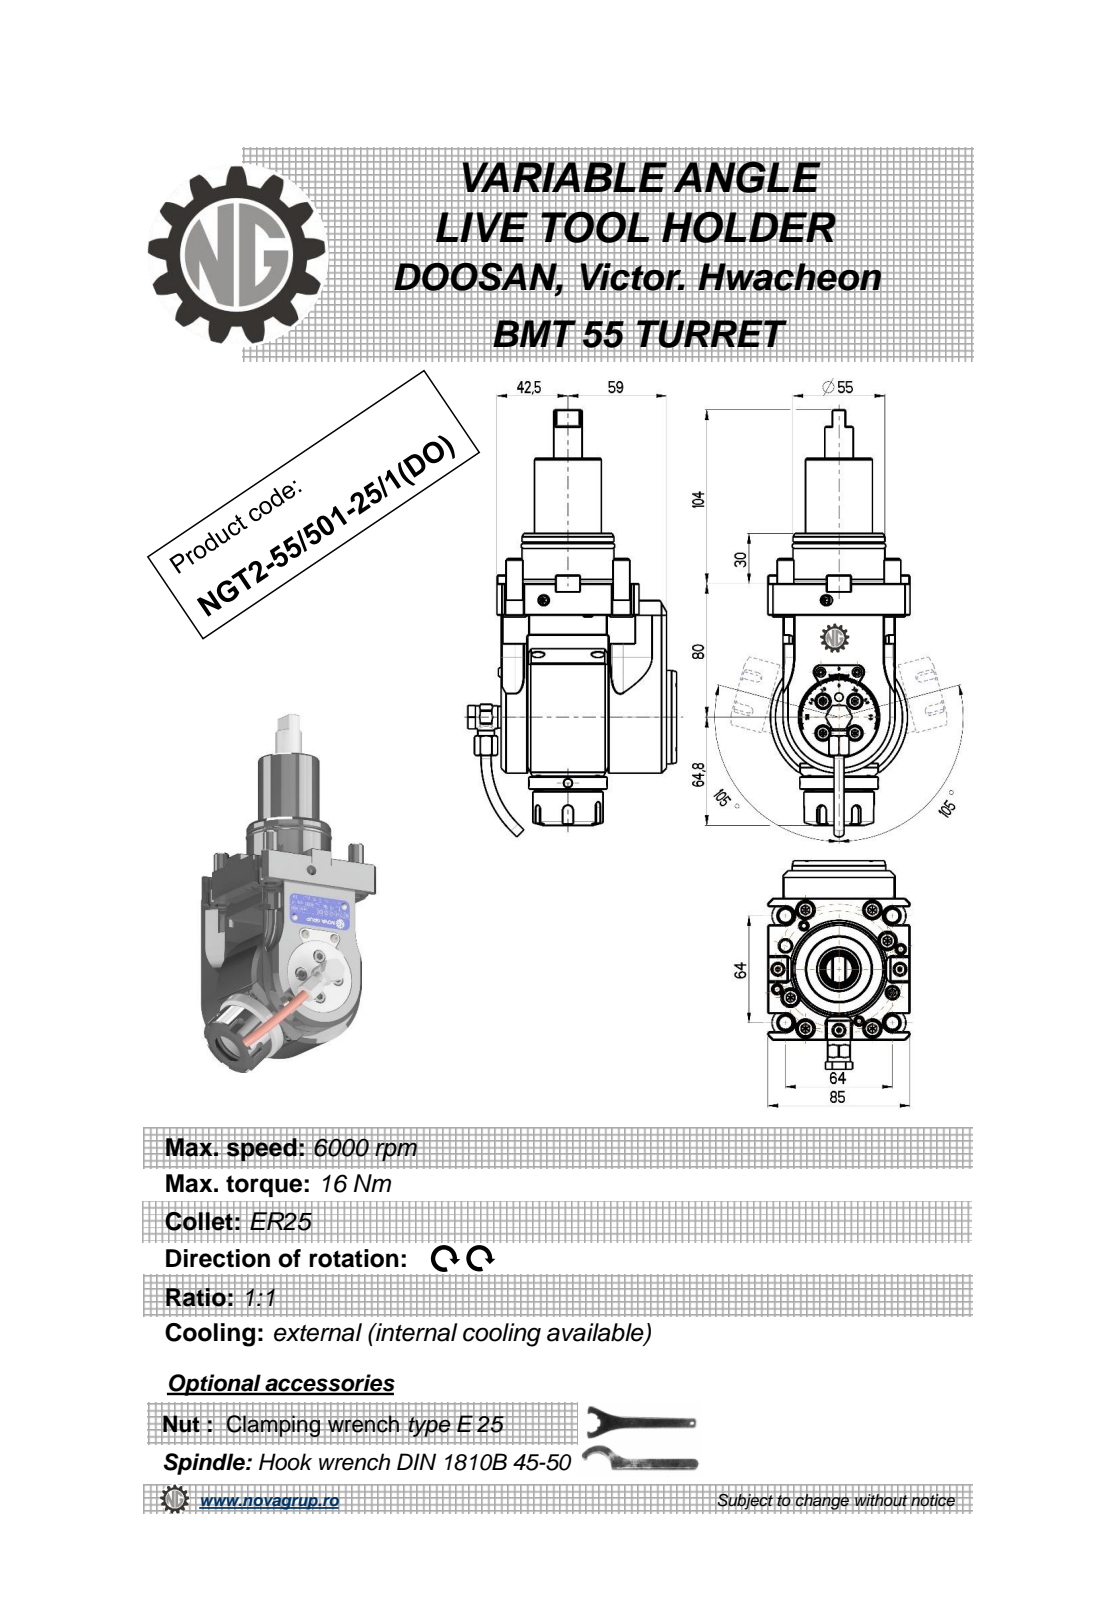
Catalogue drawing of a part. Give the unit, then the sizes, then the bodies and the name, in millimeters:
Units: millimetres
Overall size (bounding box): 255.67 × 124.9 × 85
Round holes (diameter × count): ⌀4 ×3, ⌀5 ×2, ⌀6.8 ×2, ⌀3 ×1, ⌀6.2 ×1, ⌀9 ×1, ⌀11 ×1, ⌀20.3 ×1
Round bosses / shafts (diameter × count): ⌀10 ×6, ⌀6 ×4, ⌀5.7 ×2, ⌀82 ×1, ⌀56 ×1, ⌀55 ×1, ⌀54.4 ×1, ⌀50 ×1
Partial cylindrical surfaces — rounded edges, fillets, slot ends (radius × count): R0.32 ×20, R5 ×8, R0.41 ×6, R3 ×5, R0.5 ×4, R5.5 ×4, R8 ×4, R8.5 ×4
Main face-to-face distances: 9, 31, 85, 16, 99, 66.5, 6, 18.5, 64, 2.5
Hole centre spacings: 34.93, 0.4, 39.45, 47.42, 47.72, 49, 49.4, 69.86
Volume: 902 289 mm³ · Surface area: 93 904 mm²
Bodies: 2 solids, 679 faces (301 planar, 168 cylindrical, 210 other)
Part name (STEP PRODUCT): NGT2_55_501_25_1_DO
STEP written by: PRO/ENGINEER BY PARAMETRIC TECHNOLOGY CORPORATION, 2010280 (CONFIG_CONTROL_DESIGN)
